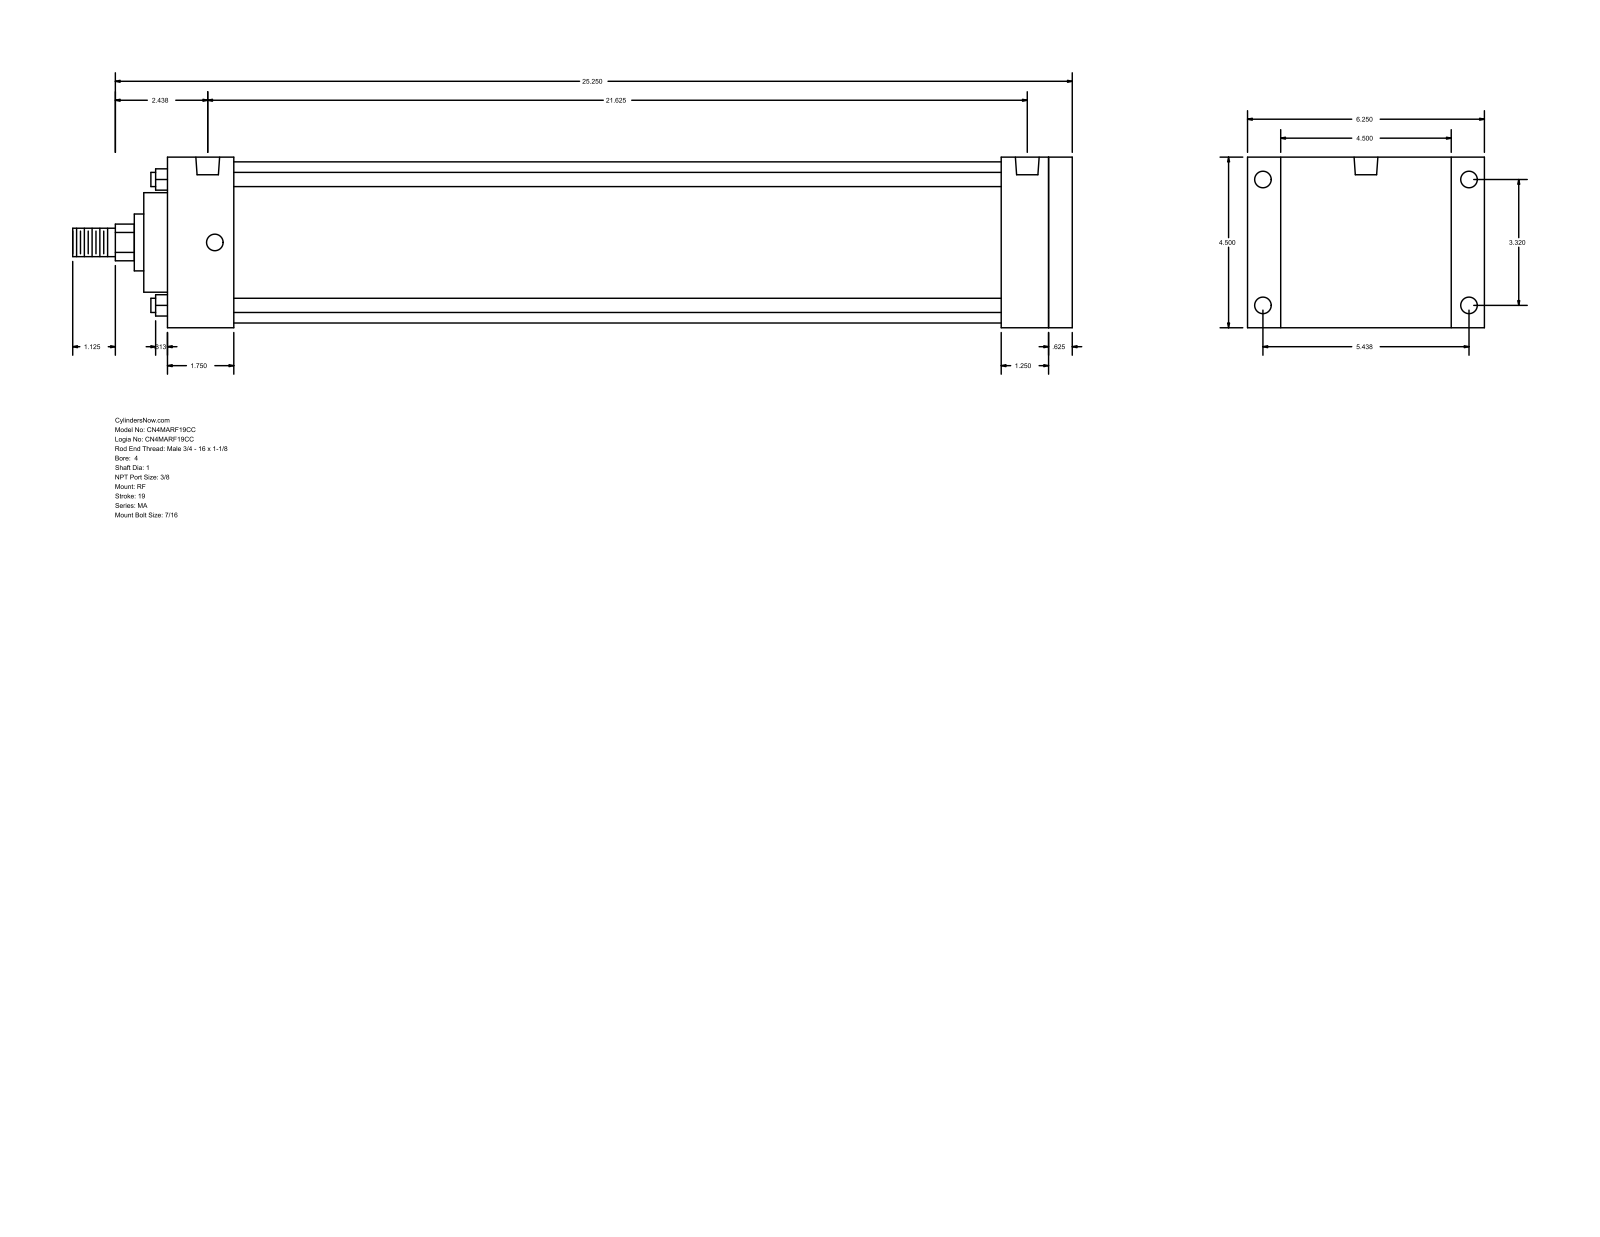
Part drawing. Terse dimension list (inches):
name: MA_RF__0400_1
written by: GSSL Pune (CONFIG_CONTROL_DESIGN)
unit: in
bodies: 0 solids, 94 faces (65 planar, 29 cylindrical, 0 other)
size: 26.375 × 6.25 × 4.5
holes: 8× ⌀0.437, 2× ⌀0.627
bosses: 4× ⌀0.375, 1× ⌀4.25, 1× ⌀2.625, 1× ⌀1.5, 1× ⌀1, 1× ⌀0.75
rounds: 1× R0.484
face distances: 4.5, 23.875, 0.625, 23.25, 1.875, 0.875, 5.375, 22, 1.25, 1.75
hole spacings: 3.32, 5.438, 6.371, 21.25, 0.187, 0.188, 21.437, 21.438
